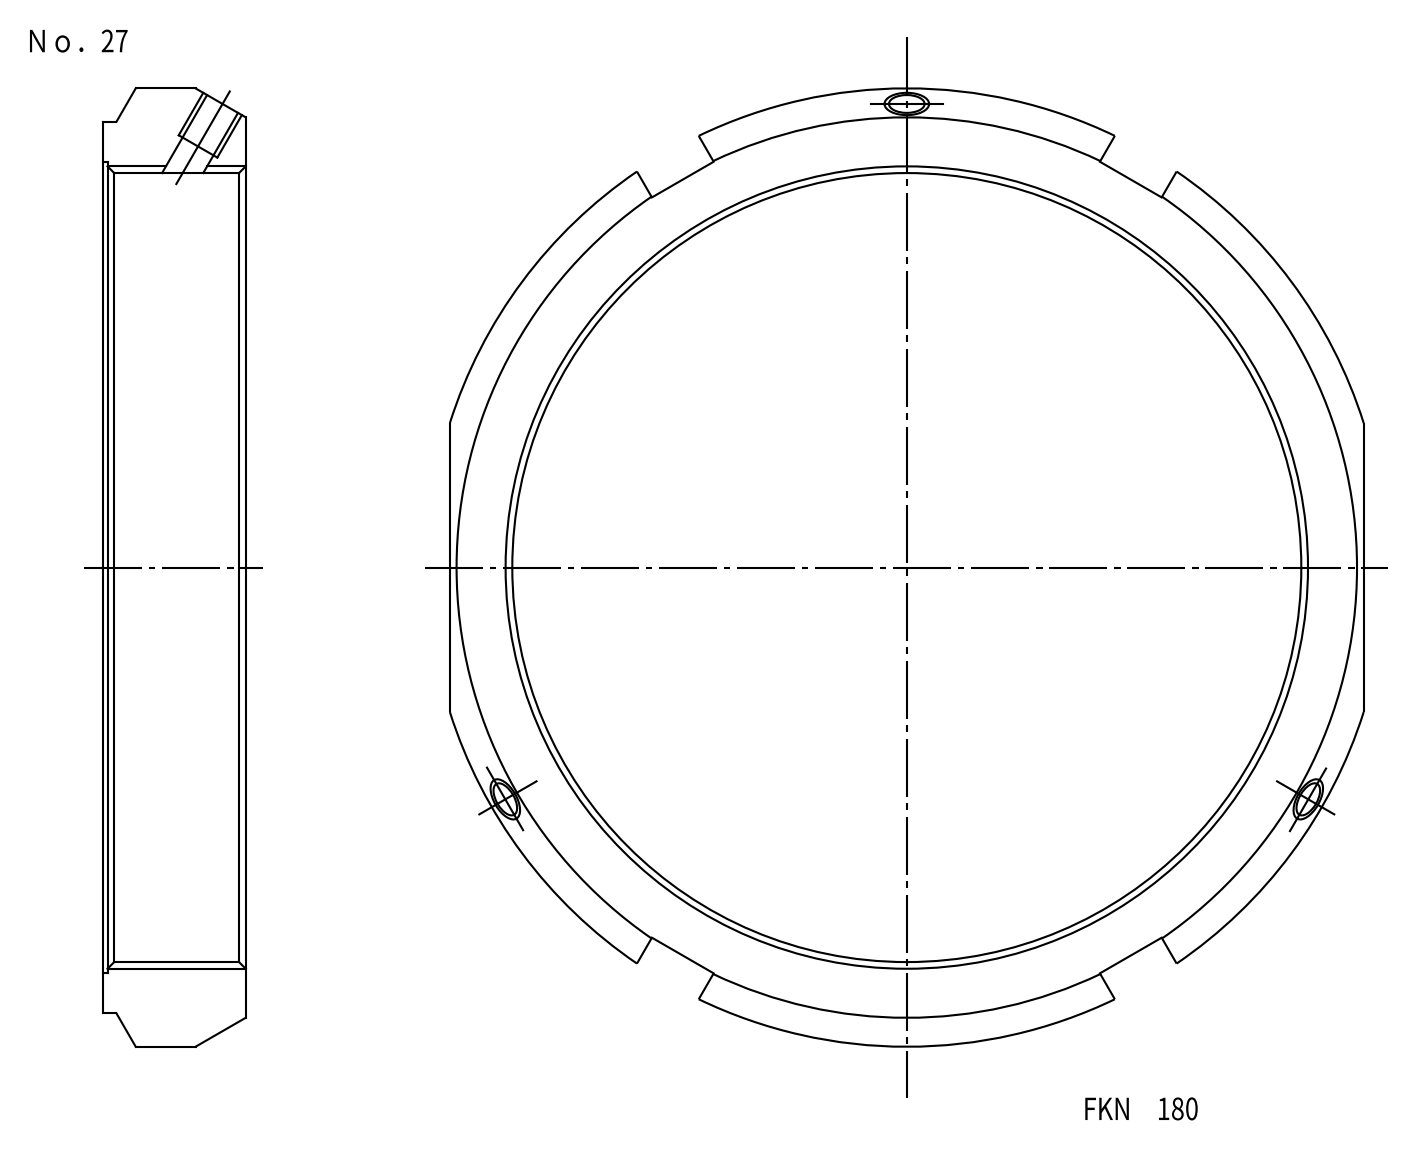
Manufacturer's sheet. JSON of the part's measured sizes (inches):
{"part_name": "FKD FKN180", "step_written_by": "Autodesk Inventor LT (CONFIG_CONTROL_DESIGN)", "units": "inches", "bodies": {"solids": 1, "faces": 40, "planar": 20, "cylindrical": 15, "other": 5}, "overall_size": [8.465, 8.071, 1.26], "volume_in3": 16.91, "surface_area_in2": 88.39, "round_holes": [[0.33, 3], [0.402, 3], [7.087, 1], [7.165, 1]], "round_bosses_or_shafts": [[7.874, 1]], "partial_cylinders_radius": [[4.232, 1]], "face_to_face_distances": [1.26, 8.071, 7.913, 0.059, 1.201, 0.63]}
